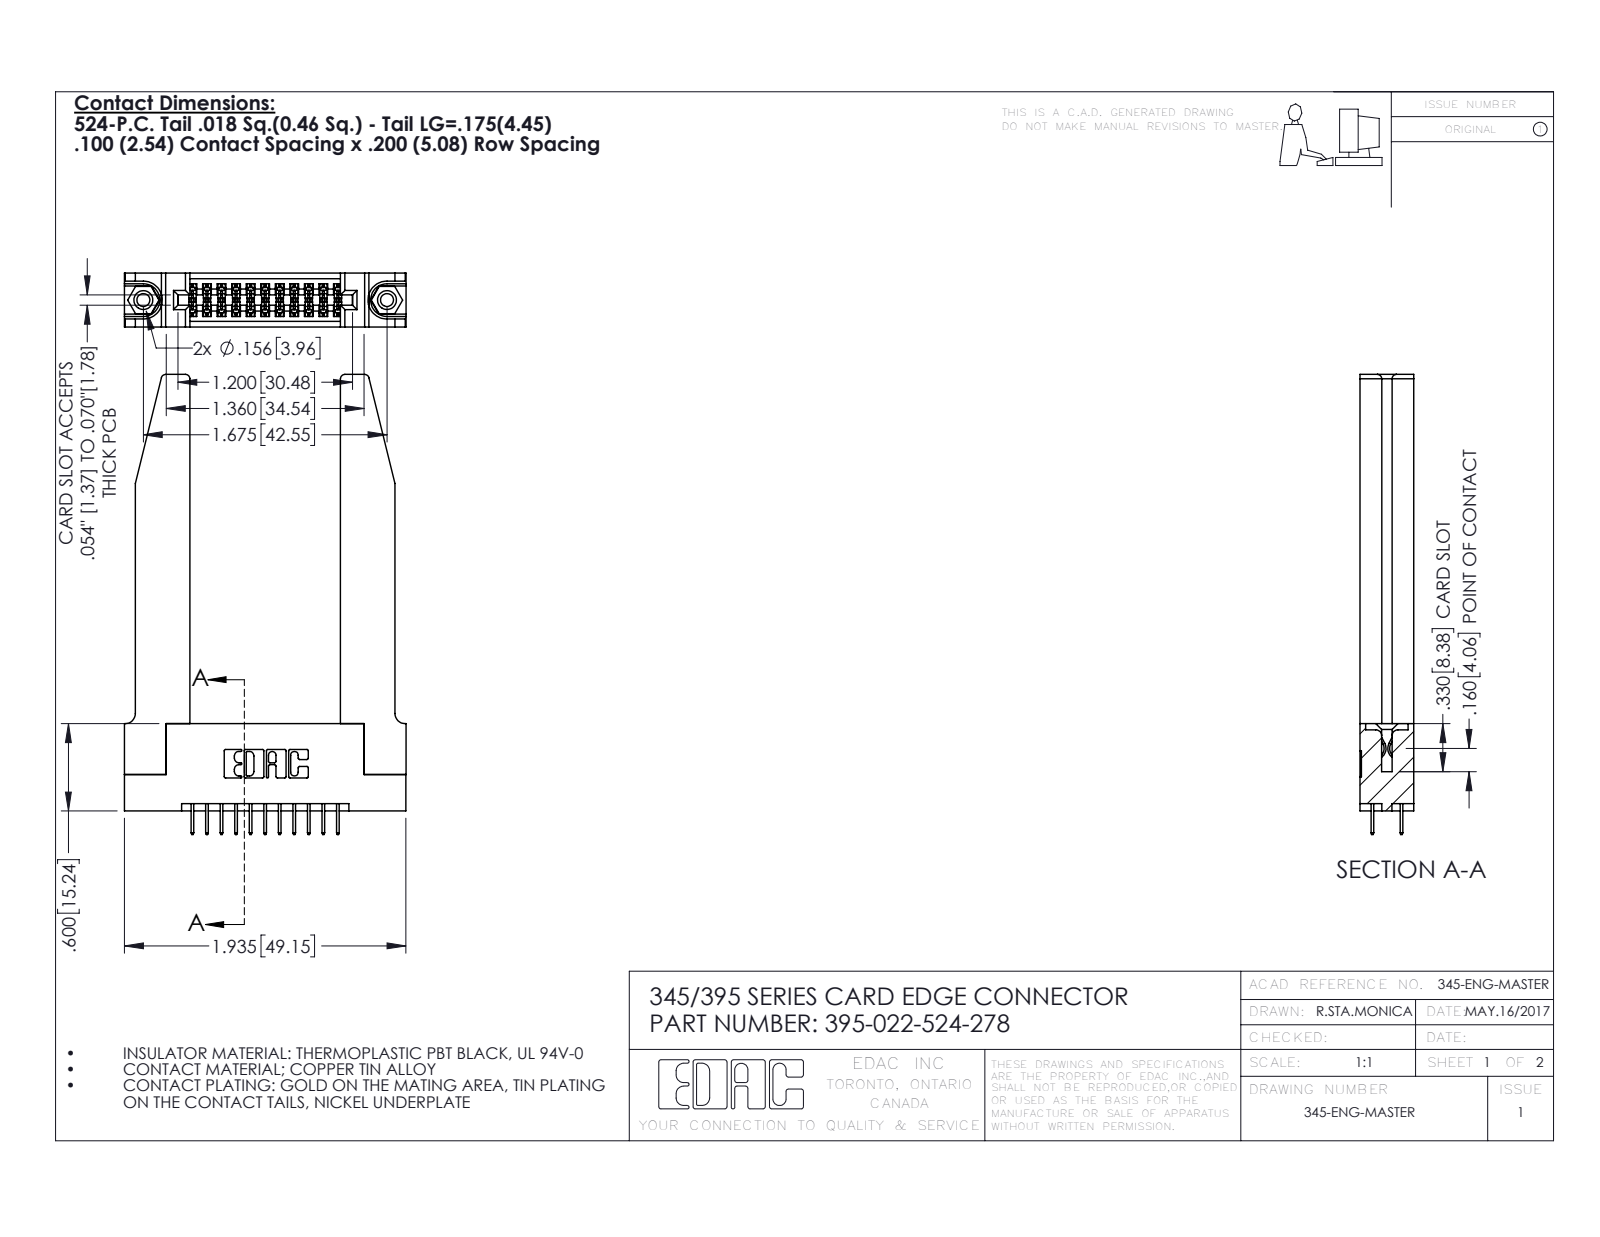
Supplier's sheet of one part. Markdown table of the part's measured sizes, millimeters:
| quantity | value |
| --- | --- |
| part name | 345-220-078_345-220-078; 345-292-001_345-293-124; 345 Part_Flush Mounting Lugs - 0.156 Dia-TH; 345-250-001_345-250-001-102 (+1 more) |
| STEP written by | SolidWorks 2016 (CONFIG_CONTROL_DESIGN) |
| units | millimeters |
| bodies | 27 solids, 1548 faces (1080 planar, 416 cylindrical, 52 other) |
| overall size | 80.3 × 49.2 × 9.4 |
| volume | 12 200 mm³ |
| surface area | 12 740 mm² |
| round holes (diameter × count) | 2.3 × 2, 3.2 × 2, 4 × 2, 1.6 × 1 |
| round bosses / shafts (diameter × count) | 3.9 × 2 |
| partial cylindrical surfaces (radius × count) | 0.2 × 33, 0.3 × 22, 0.8 × 8, 0.2 × 6, 0.8 × 6, 0.7 × 3, 0.4 × 2, 0.5 × 2 |
| main face-to-face distances | 9.4, 1.8, 7.6, 3.8, 3.8, 5.1, 2, 5.6, 26.3, 5.7 |
| hole center spacings | 6.9, 36.7, 42.5 |
